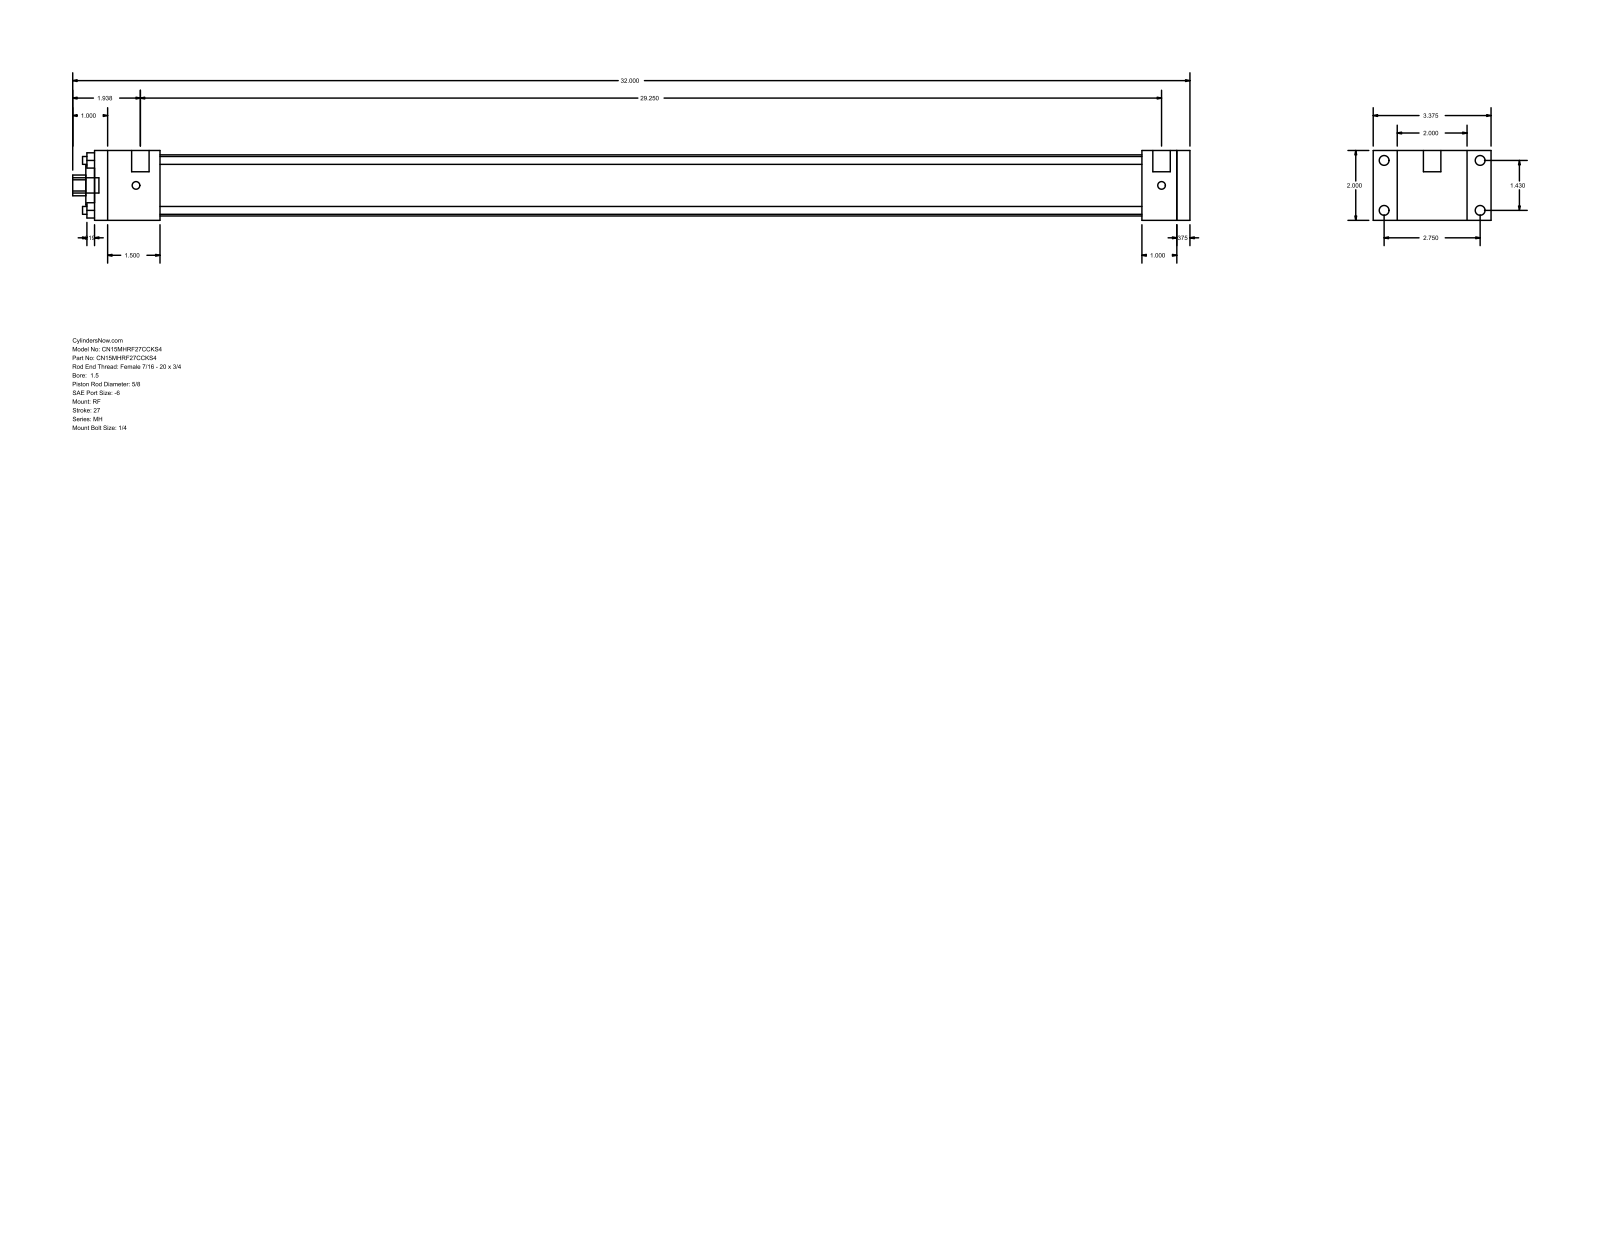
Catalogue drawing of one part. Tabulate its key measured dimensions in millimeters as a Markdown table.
| quantity | value |
| --- | --- |
| part name | MH_RF__0150_0.625 |
| STEP written by | GSSL Pune (CONFIG_CONTROL_DESIGN) |
| units | millimeters |
| bodies | 0 solids, 92 faces (64 planar, 28 cylindrical, 0 other) |
| overall size | 812.8 × 85.72 × 50.8 |
| round holes (diameter × count) | 5.71 × 4, 15.88 × 1, 28.57 × 1, 44.45 × 1 |
| round bosses / shafts (diameter × count) | 7.14 × 4, 5.56 × 4, 12.7 × 2, 11.11 × 1 |
| partial cylindrical surfaces (radius × count) | 7.54 × 1 |
| main face-to-face distances | 50.8, 9.53, 796.92, 787.39, 17.46, 68.26, 762, 25.39, 34.92, 47.62 |
| hole center spacings | 25.68, 36.32, 51.36 |
